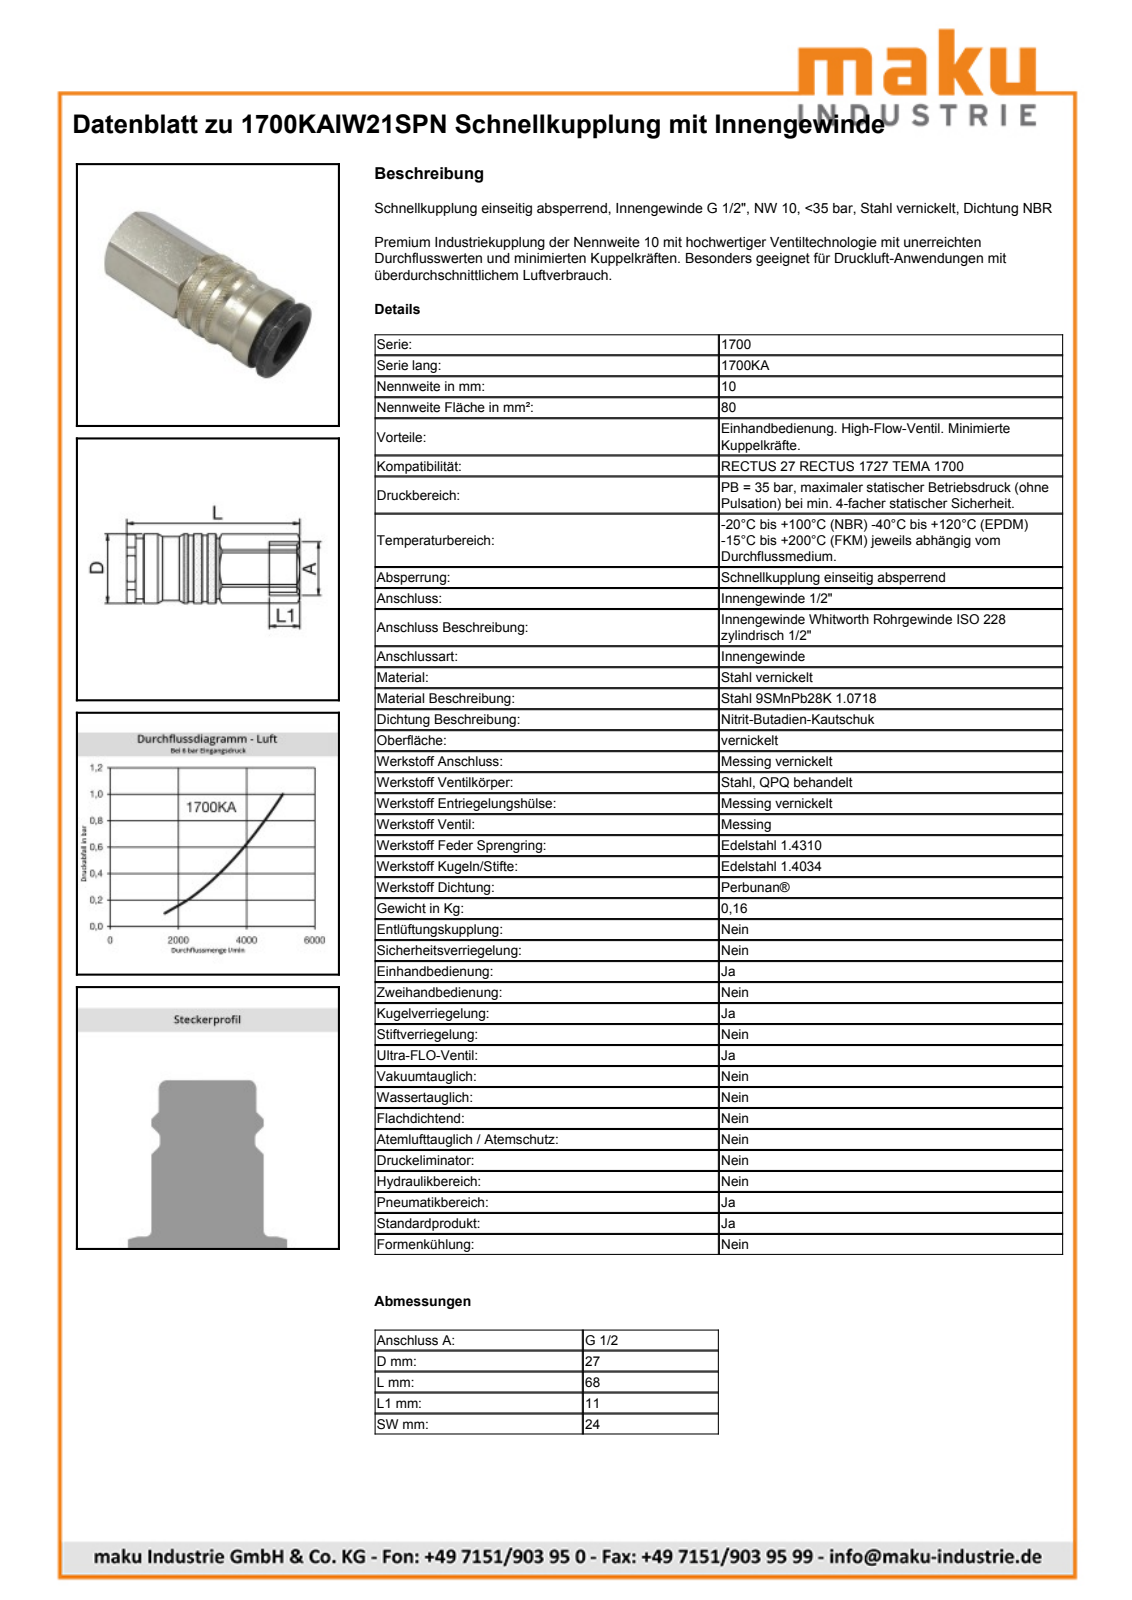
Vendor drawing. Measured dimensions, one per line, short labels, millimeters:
name: D103695
written by: Autodesk Inventor 2011 (AUTOMOTIVE_DESIGN)
unit: mm
bodies: 2 solids, 659 faces (195 planar, 90 cylindrical, 374 other)
size: 67.64 × 27.05 × 26.8
volume: 29 790 mm³; area: 12 596 mm²
holes: 1× ⌀18.63, 1× ⌀21.2, 1× ⌀21.4, 1× ⌀22.5, 1× ⌀23.8, 1× ⌀24
bosses: 1× ⌀26.8, 1× ⌀26, 1× ⌀25, 1× ⌀23.7, 1× ⌀21.3, 1× ⌀21, 1× ⌀20.97, 1× ⌀20.87
rounds: 1× R12.4, 1× R13.5, 1× R13.53
face distances: 24, 54.83, 1, 25, 67.64, 12.81, 30.64, 24.19, 37, 6.55
